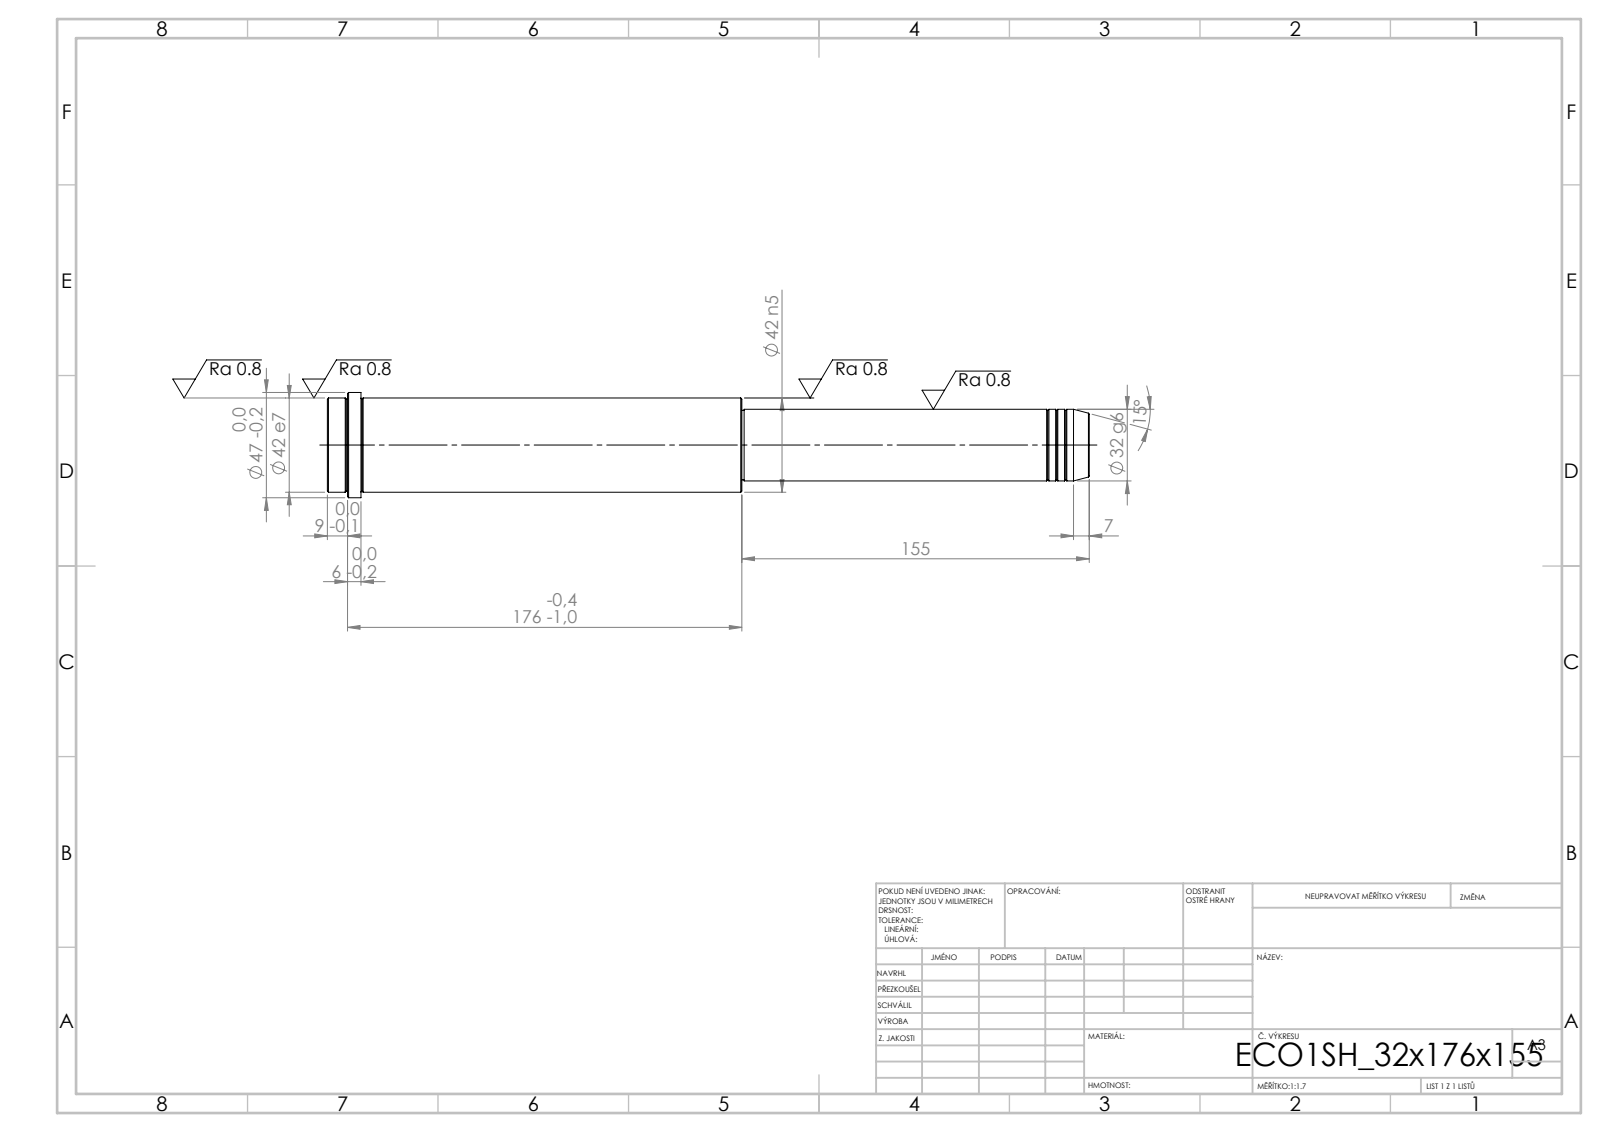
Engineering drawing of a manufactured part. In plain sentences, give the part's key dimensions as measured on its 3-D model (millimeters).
Its 3-D file was written by "SolidWorks 2019 (CONFIG_CONTROL_DESIGN)". It is 1 solid with 52 faces: 6 planar, 16 cylindrical and 30 other. Overall it measures 340 by 47 by 47 millimeters. Its volume is 382 106 cubic millimeters and its surface area 43 633 square millimeters. Round bosses or shafts: 1 of diameter 47, 1 of diameter 42, 1 of diameter 32, 1 of diameter 31. The main face-to-face distances are 340, 155, 185, 325, 170, 15, 331, 176, 6, 9.
